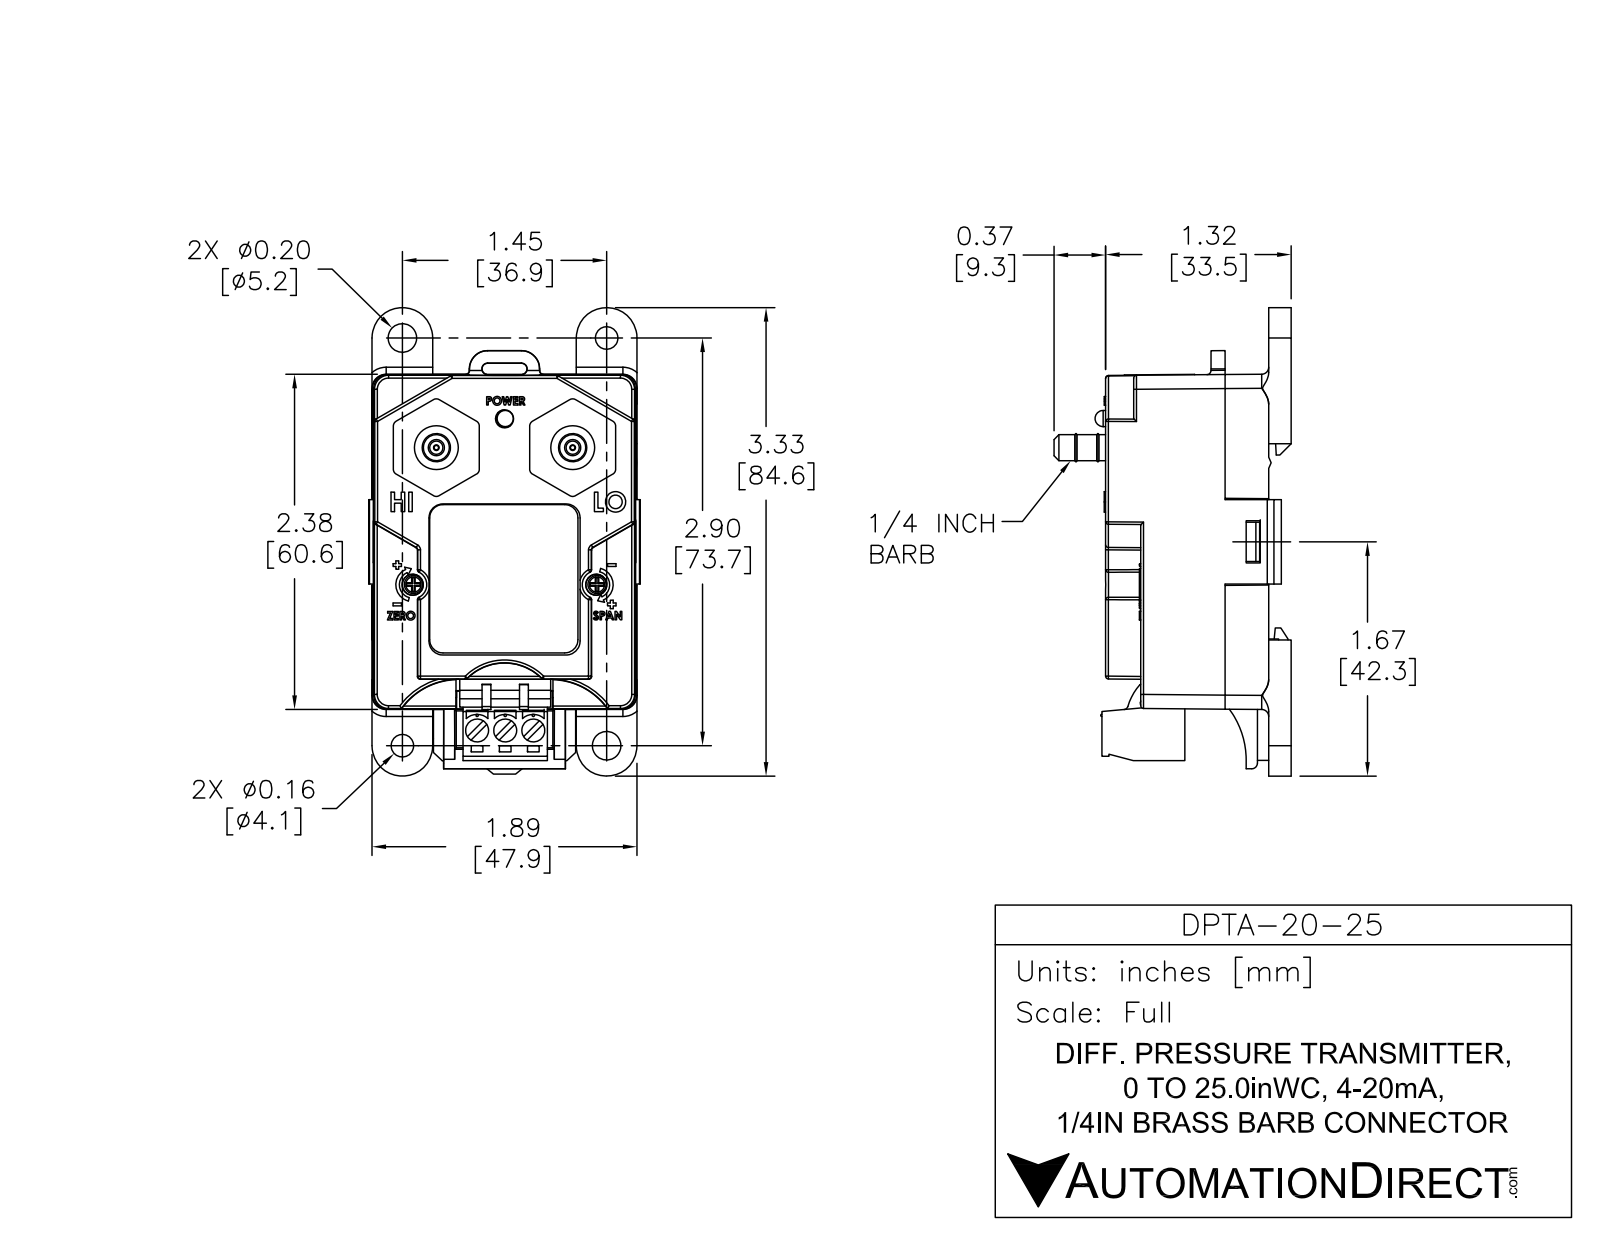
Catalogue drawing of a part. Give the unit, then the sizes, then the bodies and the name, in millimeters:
Units: millimetres
Overall size (bounding box): 85.01 × 49.76 × 43.1
Round holes (diameter × count): ⌀4 ×7, ⌀2.5 ×2, ⌀5.12 ×2, ⌀3.1 ×1
Round bosses / shafts (diameter × count): ⌀5 ×3, ⌀3.5 ×3, ⌀3.5 ×3, ⌀8 ×2, ⌀4.75 ×2, ⌀3 ×1
Partial cylindrical surfaces — rounded edges, fillets, slot ends (radius × count): R3 ×12, R2 ×4, R5.5 ×4, R0.99 ×2, R1.06 ×2, R1.12 ×2, R2.38 ×2, R3.25 ×2
Main face-to-face distances: 1, 1.9, 4, 29.1, 0.5, 46.9, 5.9, 5, 33.1, 27.2
Hole centre spacings: 13.55, 20.73, 23.37, 24.92, 29.43, 34.46, 36.67, 38.22
Volume: 29 684 mm³ · Surface area: 34 743 mm²
Bodies: 11 solids, 448 faces (354 planar, 85 cylindrical, 9 other)
Part name (STEP PRODUCT): DPTA-20-25
STEP written by: SolidWorks 2011 (AUTOMOTIVE_DESIGN)
